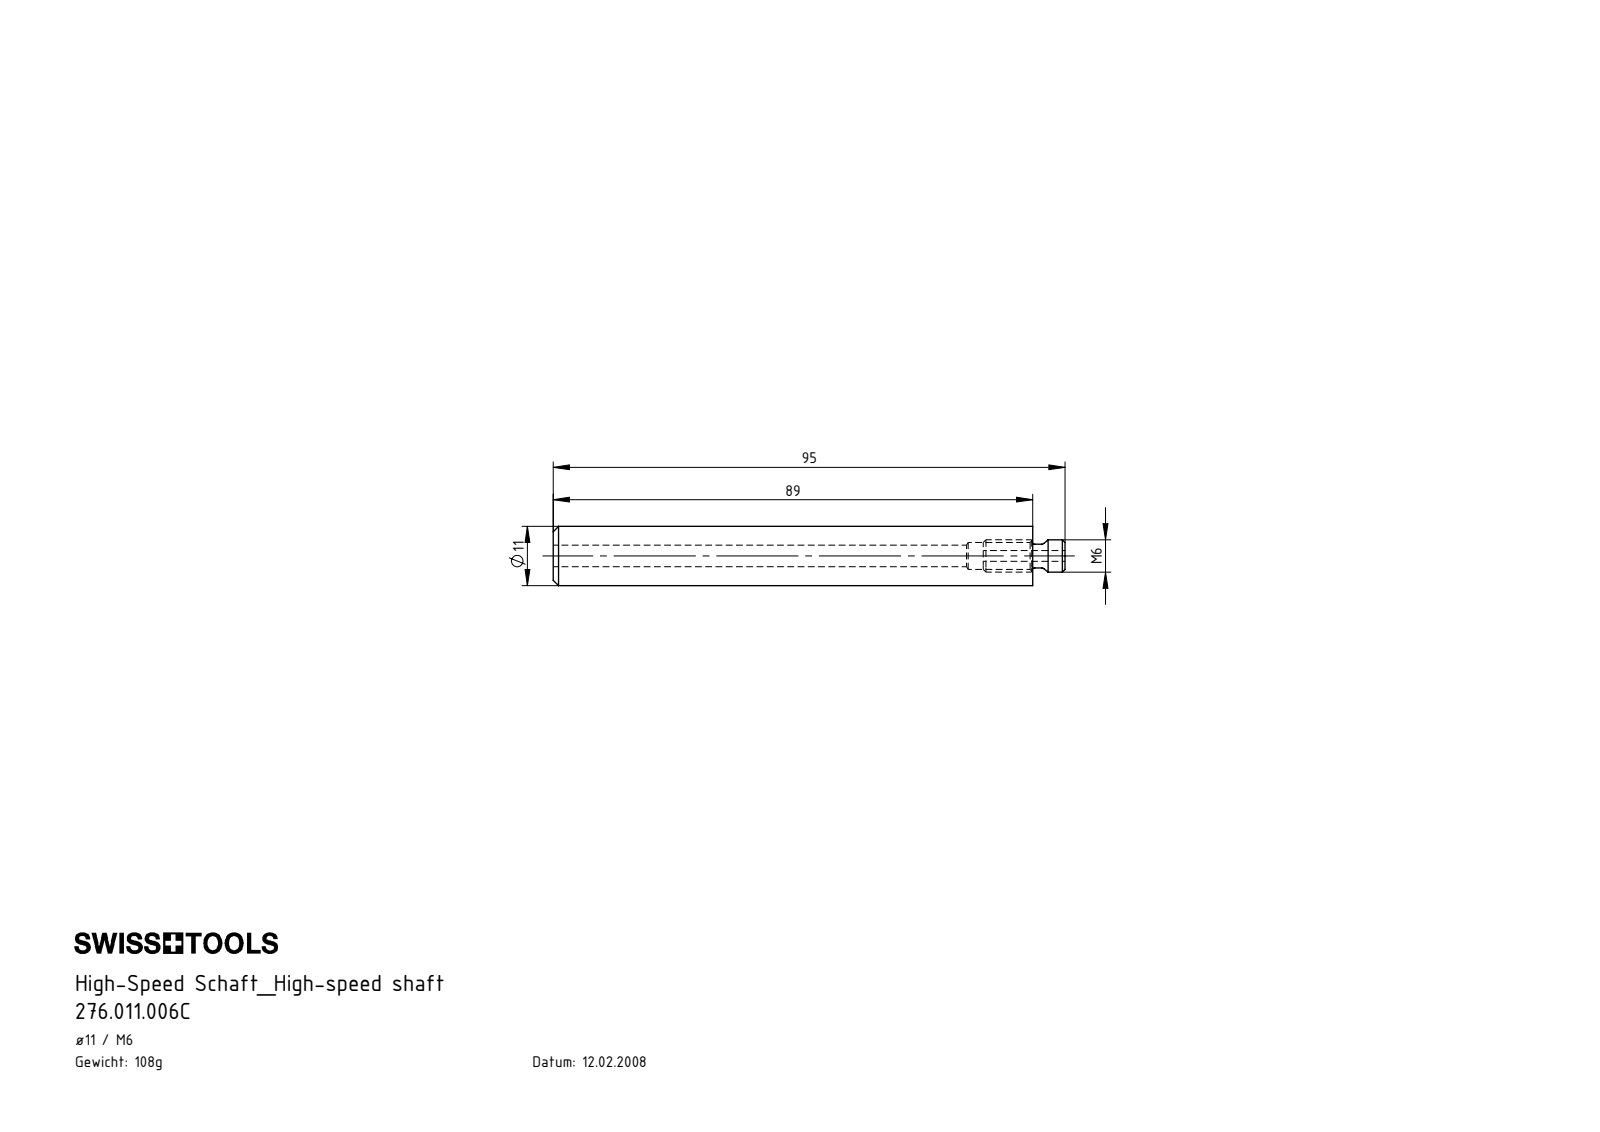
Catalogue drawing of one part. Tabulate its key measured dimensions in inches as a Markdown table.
| quantity | value |
| --- | --- |
| part name | HM1-BG1.006.015_A; 276.011.006C; HM1-U11.001.089_A |
| STEP written by | SolidWorks 2022 (CONFIG_CONTROL_DESIGN) |
| units | inches |
| bodies | 2 solids, 35 faces (5 planar, 14 cylindrical, 16 other) |
| overall size | 3.74 × 0.433 × 0.433 |
| volume | 0.463 in³ |
| surface area | 7.425 in² |
| round holes (diameter × count) | 0.079 × 1, 0.157 × 1, 0.197 × 1 |
| round bosses / shafts (diameter × count) | 0.433 × 1, 0.236 × 1, 0.173 × 1 |
| main face-to-face distances | 3.504, 3.74, 0.236, 3.142, 0.362, 0.598, 3.496, 0.354, 0.244 |
